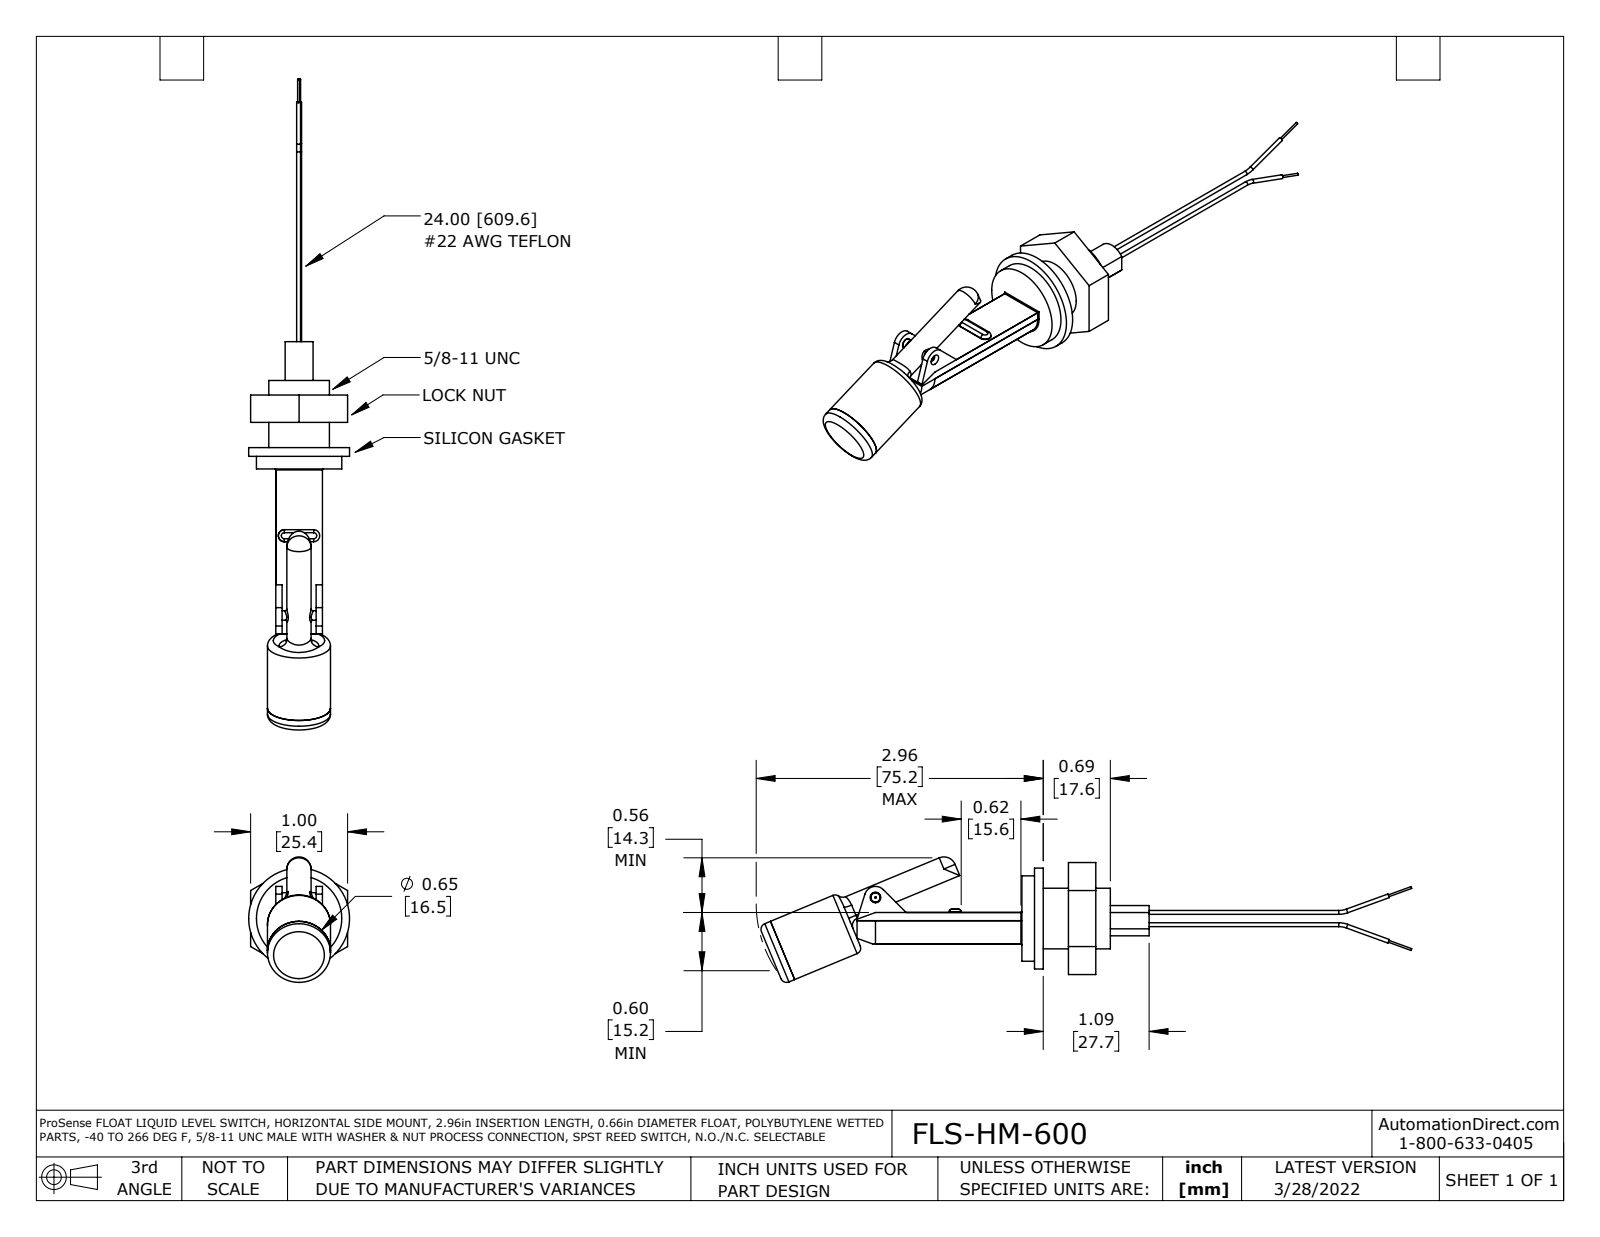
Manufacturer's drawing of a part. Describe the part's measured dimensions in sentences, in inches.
The part is named "ADM7790 nc w ext1B coord red1 r1 fxtaN". Its 3-D file was written by "SolidWorks 2021 (AUTOMOTIVE_DESIGN)". It is 9 solids with 169 faces: 63 planar, 60 cylindrical and 46 other. Overall it measures 6.711 by 1.294 by 1.04 inches. Its volume is 1.212 cubic inches and its surface area 20.41 square inches. Round holes: 1 of diameter 0.01, 1 of diameter 0.11, 1 of diameter 0.45, 1 of diameter 0.5, 1 of diameter 0.53, 1 of diameter 0.56, 1 of diameter 0.62, 1 of diameter 0.625. Round bosses or shafts: 4 of diameter 0.04, 2 of diameter 0.65, 2 of diameter 0.02, 1 of diameter 1.04, 1 of diameter 0.88, 1 of diameter 0.55, 1 of diameter 0.25, 1 of diameter 0.125. Partial cylindrical surfaces (rounded edges, fillets, slot ends): 2 of radius 0.01, 2 of radius 0.031, 2 of radius 0.062, 2 of radius 0.18, 1 of radius 0.114, 1 of radius 0.125, 1 of radius 0.241. The main face-to-face distances are 0.13, 0.632, 0.762, 0.282, 0.35, 0.48, 0.542, 0.26, 0.09, 0.22. The hole center spacings are 0.064.
